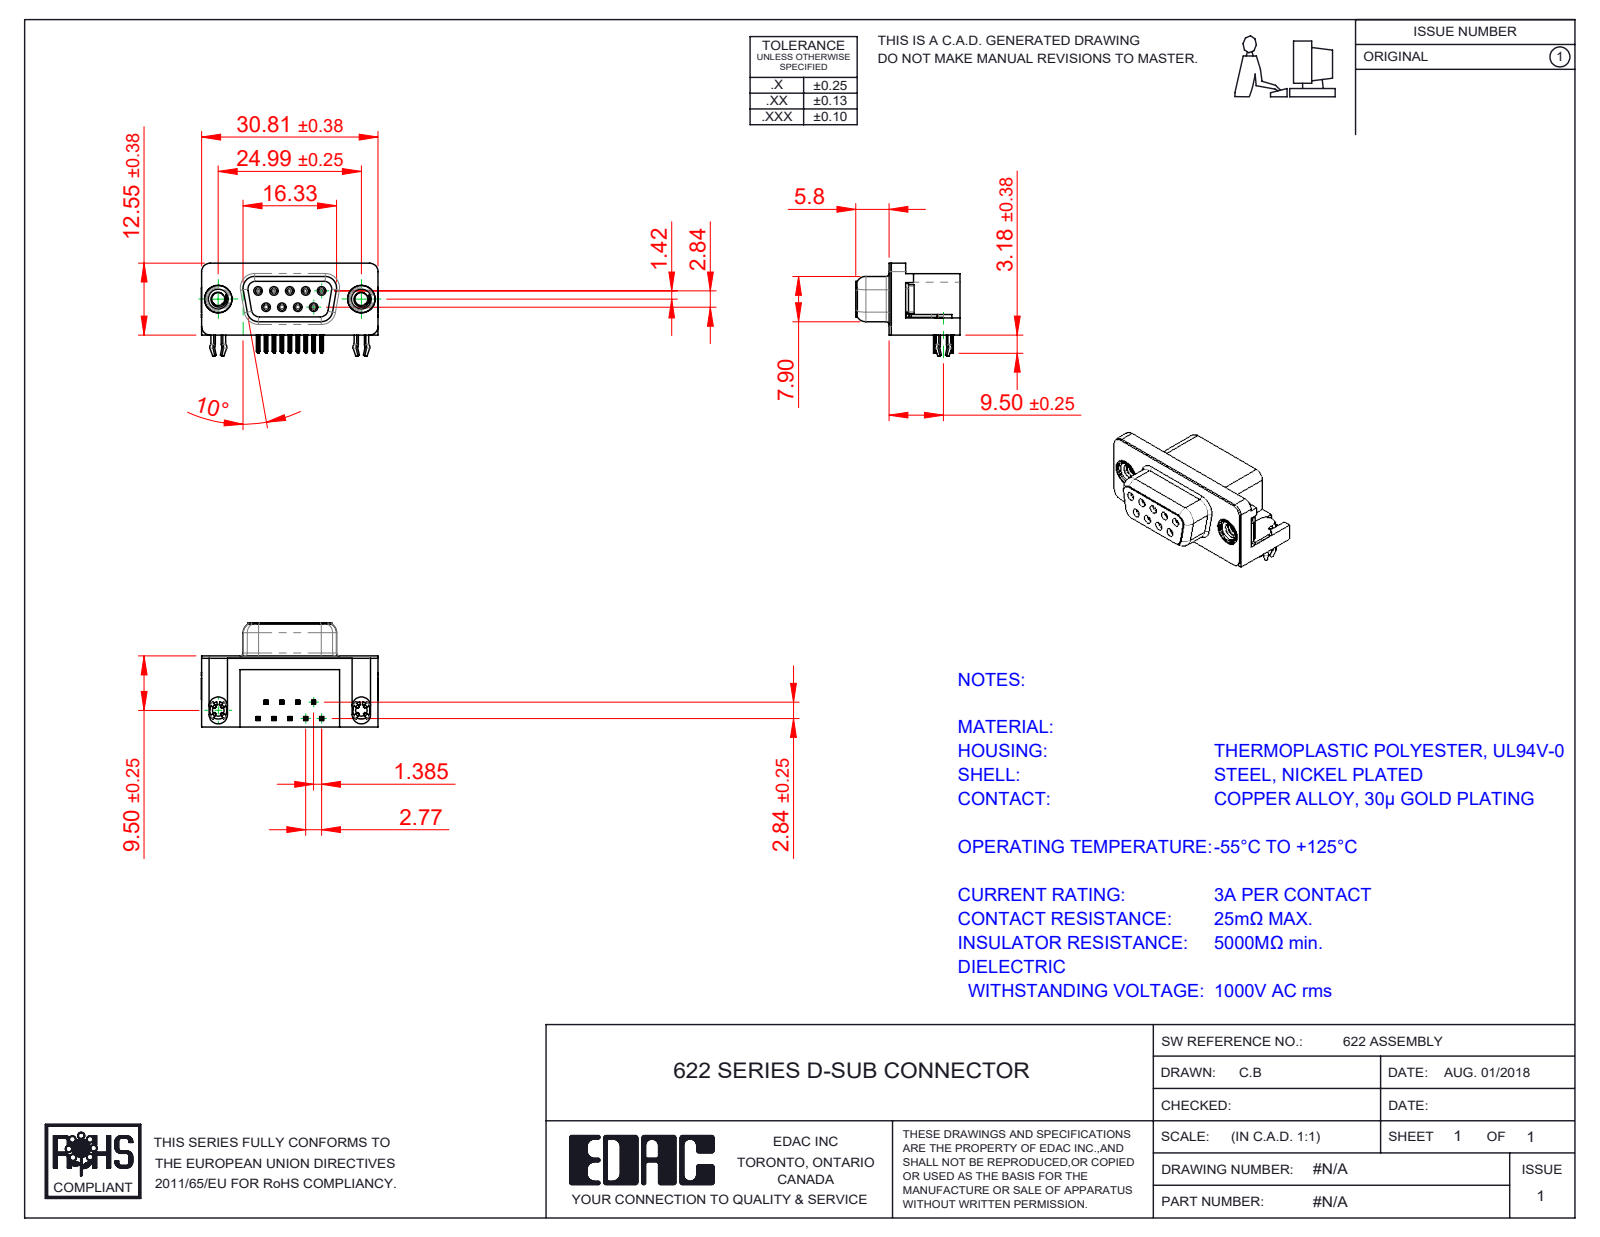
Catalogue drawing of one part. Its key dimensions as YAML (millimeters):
part_name: "622 4-40 Threaded Board Mount; 622 Socket Bottom; 622 Shell_9 Socket; 622 Housing_9 Socket (+3 more)"
step_written_by: "SolidWorks 2016 (CONFIG_CONTROL_DESIGN)"
units: millimeters
bodies: {solids: 15, faces: 1602, planar: 684, cylindrical: 428, other: 490}
overall_size: [30.89, 18.2, 15.73]
volume: 3738
surface_area: 5153
round_holes:
  - {diameter: 0.8, count: 9}
  - {diameter: 0.9, count: 9}
  - {diameter: 2.26, count: 4}
  - {diameter: 4, count: 2}
  - {diameter: 4.8, count: 2}
  - {diameter: 5, count: 2}
round_bosses_or_shafts:
  - {diameter: 1.2, count: 9}
  - {diameter: 4.9, count: 2}
  - {diameter: 4.75, count: 2}
  - {diameter: 3.9, count: 2}
  - {diameter: 3.26, count: 2}
partial_cylinders:
  - {radius: 0.1, count: 72}
  - {radius: 0.15, count: 36}
  - {radius: 0.35, count: 18}
  - {radius: 1, count: 18}
  - {radius: 0.34, count: 9}
  - {radius: 0.25, count: 8}
  - {radius: 1.35, count: 8}
  - {radius: 1.6, count: 8}
face_to_face_distances: [0.4, 12, 12.4, 0.35, 2.9, 2.5, 6.2, 10.34, 9.5, 5.8]
hole_center_spacings: [3.16, 2.77, 5.54, 5.03, 5.04, 8.31, 7.48, 7.49]
